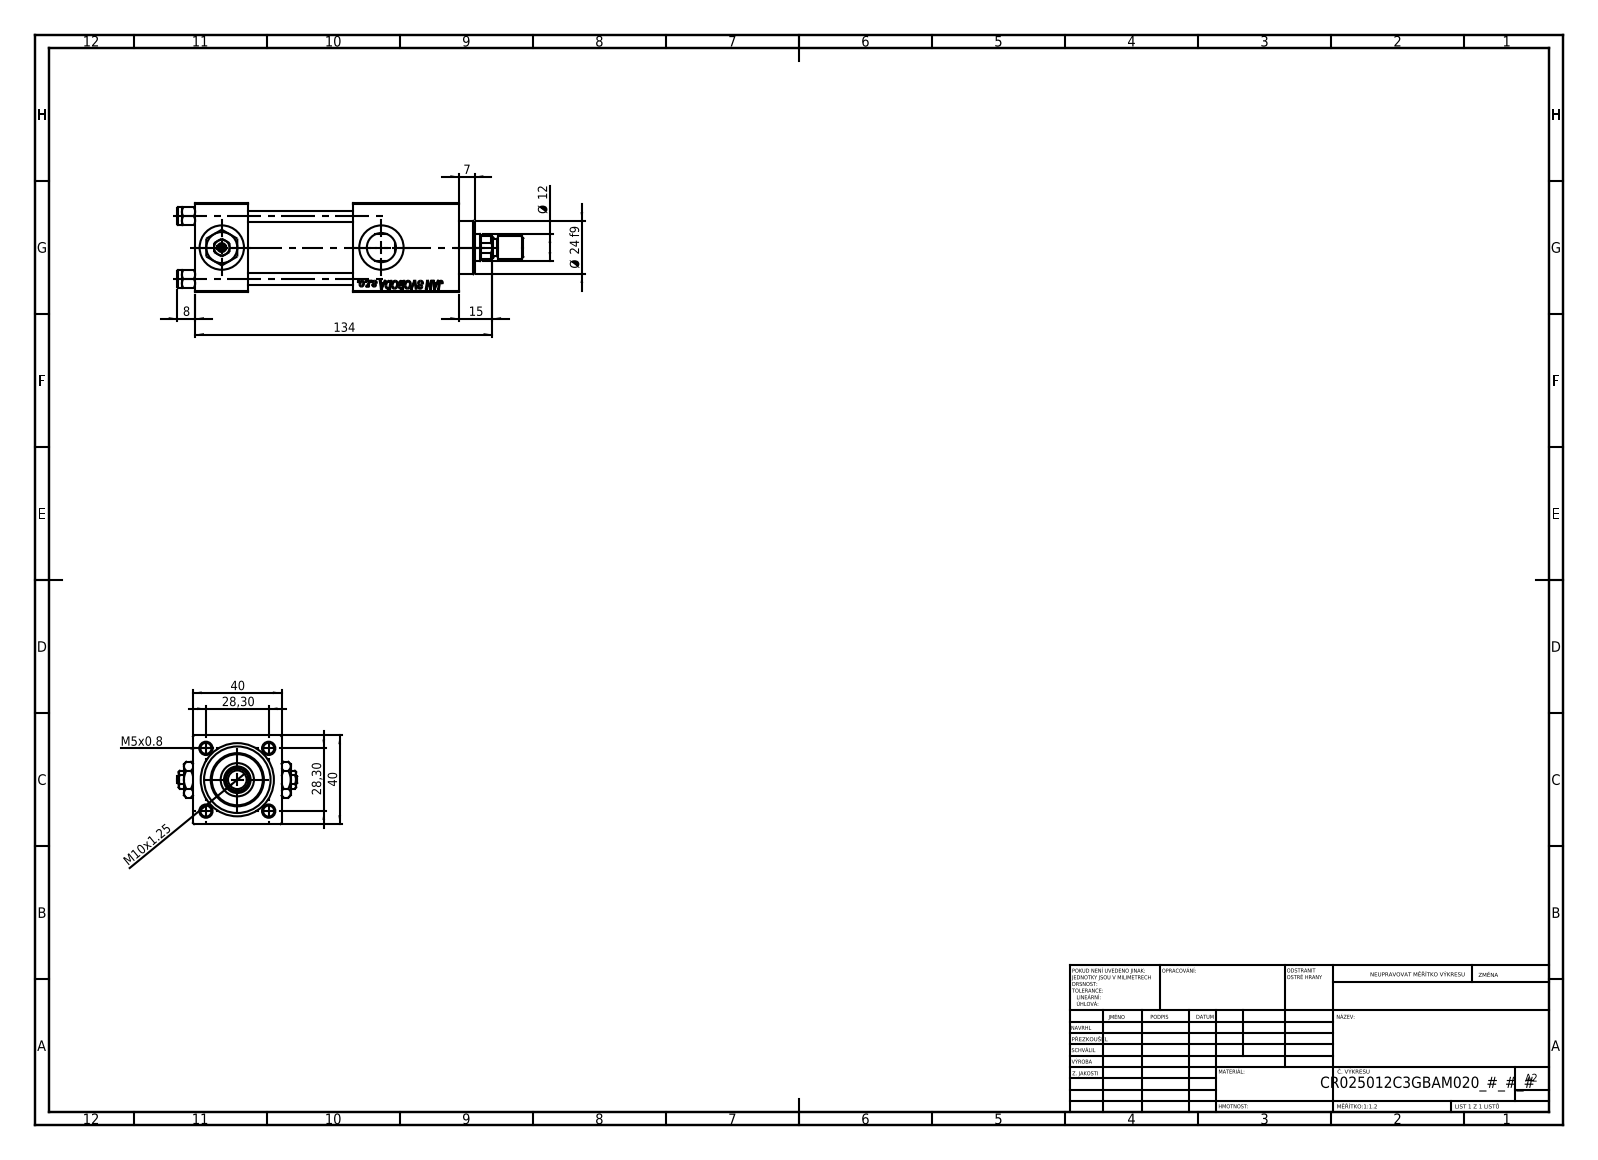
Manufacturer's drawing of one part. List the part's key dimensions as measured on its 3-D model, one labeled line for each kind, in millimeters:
Part name (STEP PRODUCT): ROD_END_AH; V215_VC_A; NUT_M5_C; V215CR_C_TYCINKA (+3 more)
STEP written by: SolidWorks 2019 (CONFIG_CONTROL_DESIGN)
Units: millimetres
Bodies: 14 solids, 1262 faces (576 planar, 102 cylindrical, 584 other)
Overall size (bounding box): 156 × 54 × 40
Volume: 142 017 mm³ · Surface area: 56 820 mm²
Round holes (diameter × count): ⌀5 ×4, ⌀20 ×3, ⌀7 ×2, ⌀13.16 ×2, ⌀6.5 ×1, ⌀12 ×1, ⌀15 ×1, ⌀25 ×1, ⌀30 ×1
Round bosses / shafts (diameter × count): ⌀8 ×5, ⌀31 ×1, ⌀24 ×1, ⌀10 ×1
Partial cylindrical surfaces — rounded edges, fillets, slot ends (radius × count): R5.5 ×1
Main face-to-face distances: 40, 24, 39.8, 48, 90.3, 66.3, 71, 47, 19.3, 119
Hole centre spacings: 20.01, 28.3, 40.02, 72
